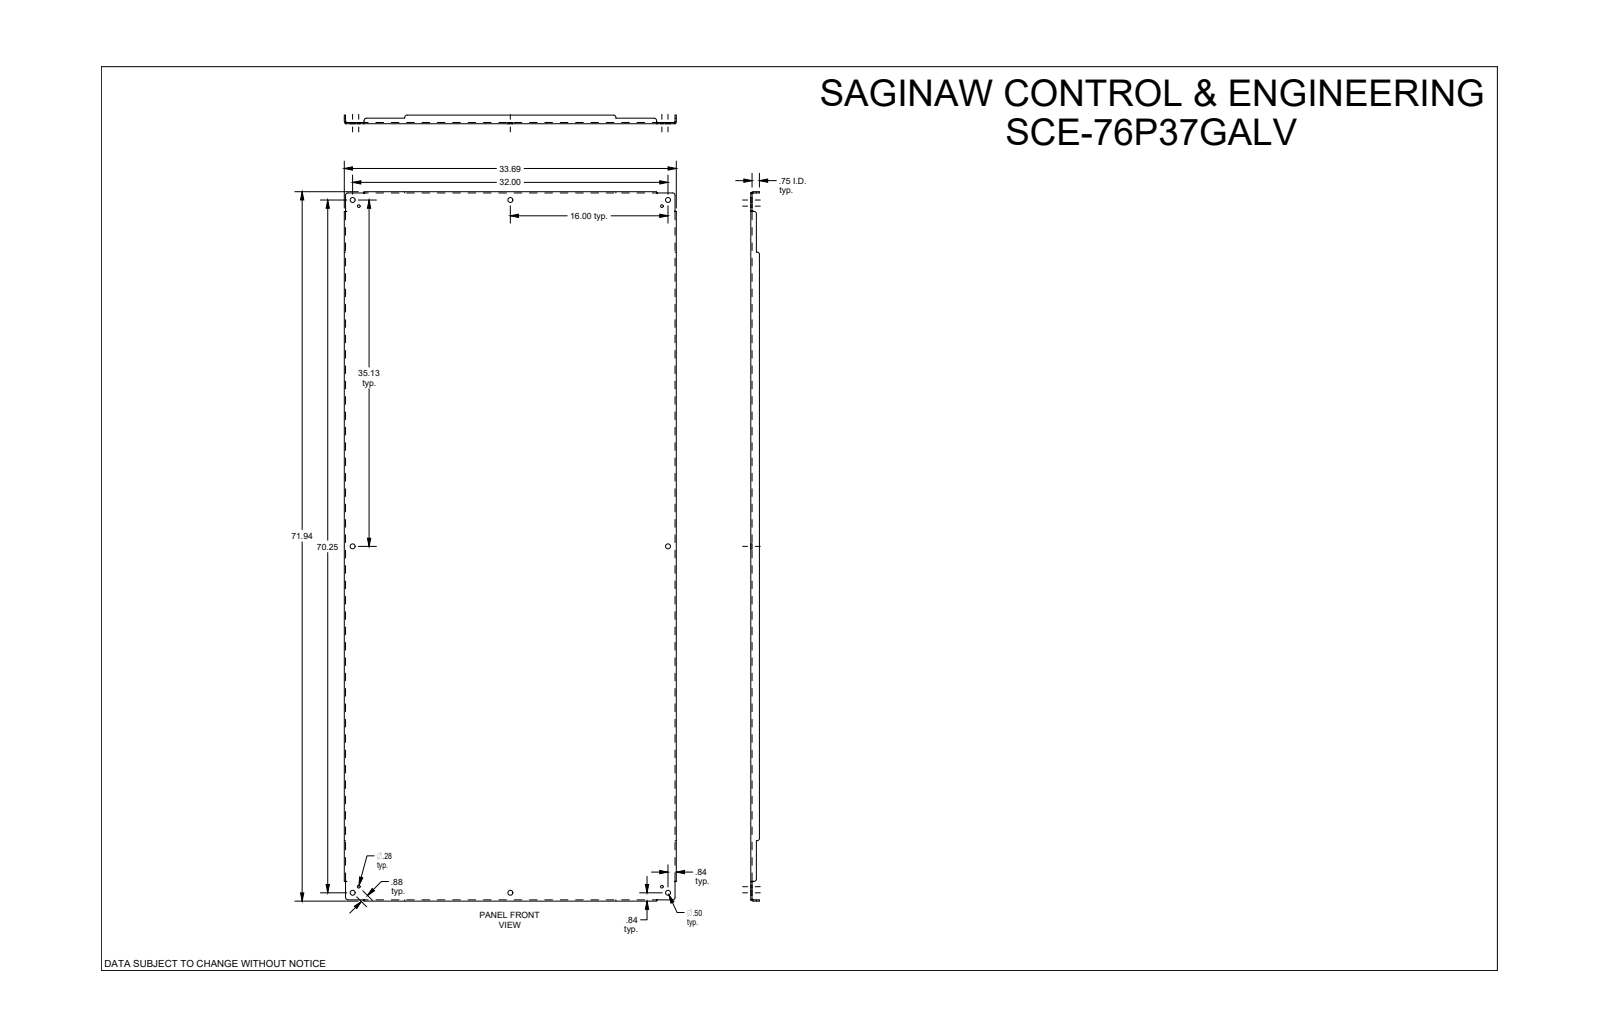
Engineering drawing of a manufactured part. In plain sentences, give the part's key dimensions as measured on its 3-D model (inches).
The part is named "SCE-76P37GALV". Its 3-D file was written by "SolidWorks 2019 (CONFIG_CONTROL_DESIGN)". It is 1 solid with 110 faces: 46 planar, 40 cylindrical and 24 other. Overall it measures 71.938 by 33.688 by 0.875 inches. Its volume is 317.6 cubic inches and its surface area 5 111 square inches. Round holes: 8 of diameter 0.5, 4 of diameter 0.281. Partial cylindrical surfaces (rounded edges, fillets, slot ends): 12 of radius 0.25, 4 of radius 0.112, 4 of radius 0.237. The main face-to-face distances are 0.125, 33.563, 33.438, 33.687, 0.125, 71.813, 0.75, 0.875, 71.687, 71.938. The hole center spacings are 0.875, 15.394, 16, 31.387, 34.512, 35.125, 38.597, 46.642.
